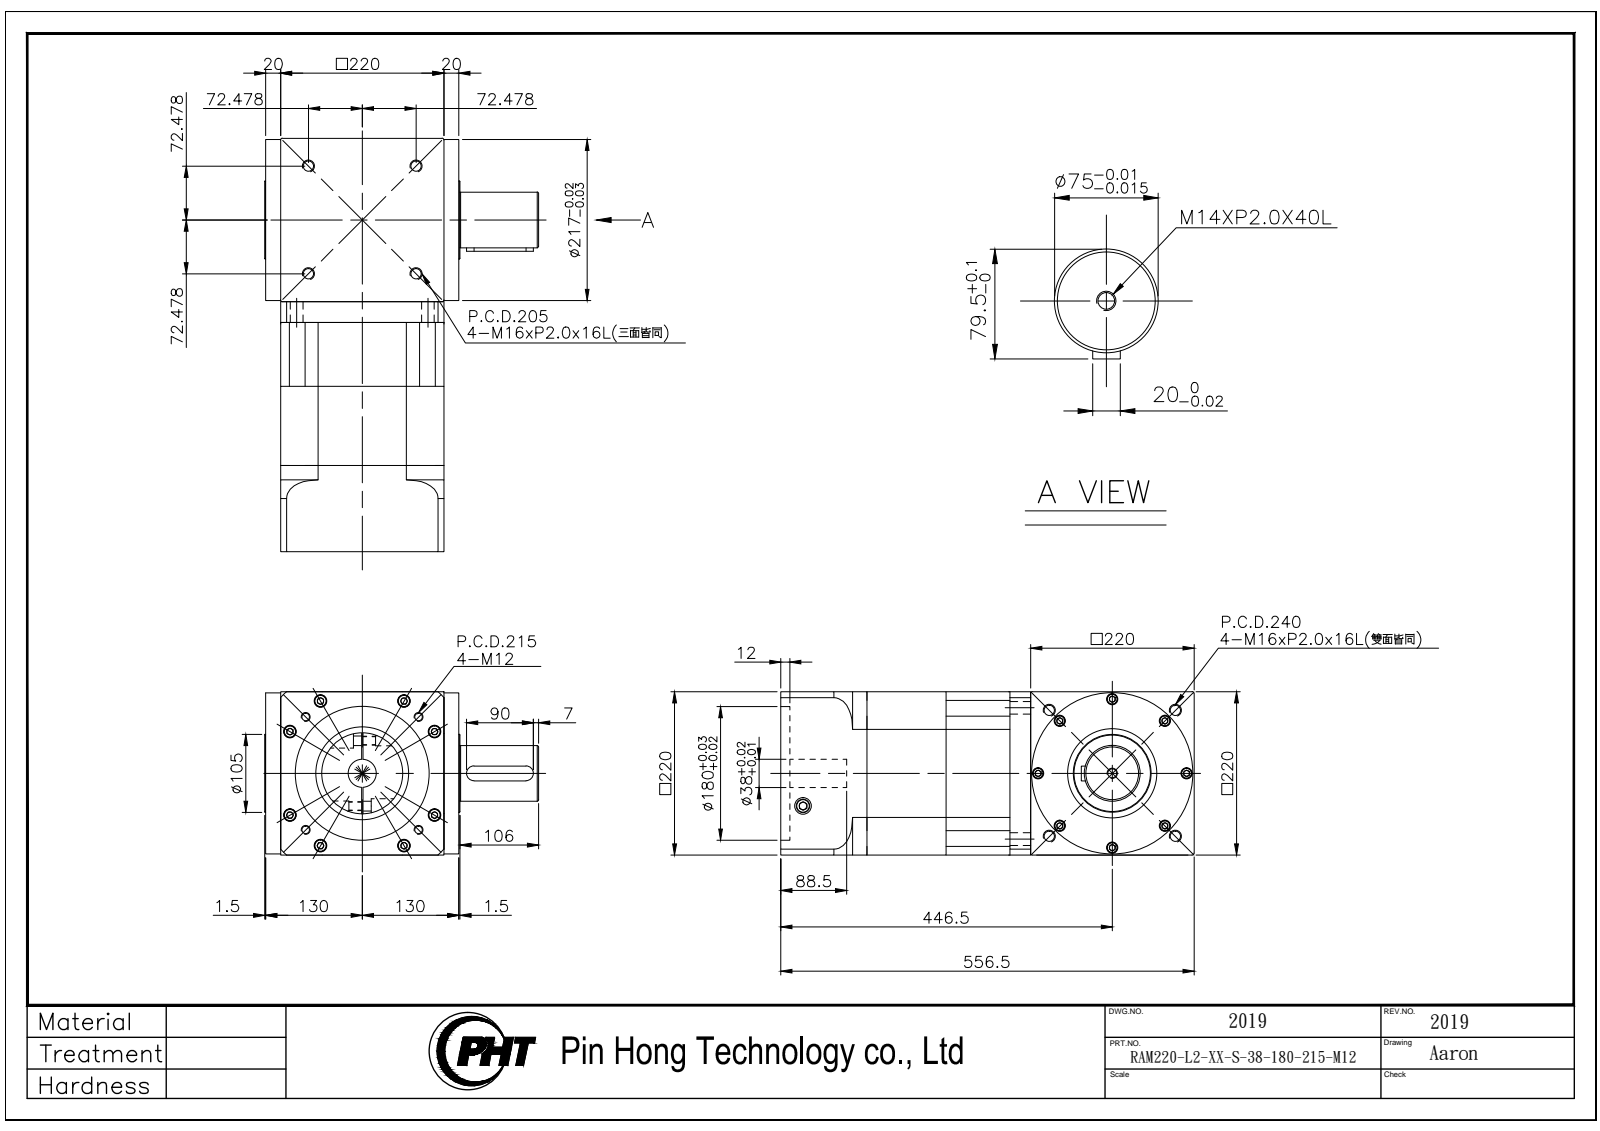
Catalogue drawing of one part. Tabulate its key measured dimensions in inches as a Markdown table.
| quantity | value |
| --- | --- |
| part name | RAM220-L2-XX-S-38-180-215-M12_2019 |
| STEP written by | SolidWorks 2016 (AUTOMOTIVE_DESIGN) |
| units | inches |
| bodies | 5 solids, 975 faces (448 planar, 325 cylindrical, 202 other) |
| overall size | 21.909 × 14.528 × 8.661 |
| volume | 1 668 in³ |
| surface area | 1 848 in² |
| round holes (diameter × count) | 0.354 × 12, 0.551 × 12, 0.591 × 12, 0.669 × 12, 0.433 × 8, 0.402 × 4, 0.886 × 2, 0.157 × 1, 0.472 × 1, 1.496 × 1, 4.921 × 1, 7.087 × 1 |
| round bosses / shafts (diameter × count) | 0.512 × 12, 0.63 × 8, 0.945 × 4, 8.543 × 1, 4.724 × 1, 4.291 × 1, 4.134 × 1, 2.953 × 1 |
| partial cylindrical surfaces (radius × count) | 0.591 × 4, 0.394 × 2, 4.921 × 1, 5.906 × 1 |
| main face-to-face distances | 8.661, 7.579, 4.193, 3.386, 8.681, 4.488, 1.102, 9.764, 17.343, 13.15 |
| hole center spacings | 3.937, 2.038, 4.429, 5.568, 6.819, 7.606, 1.147, 1.172 |
